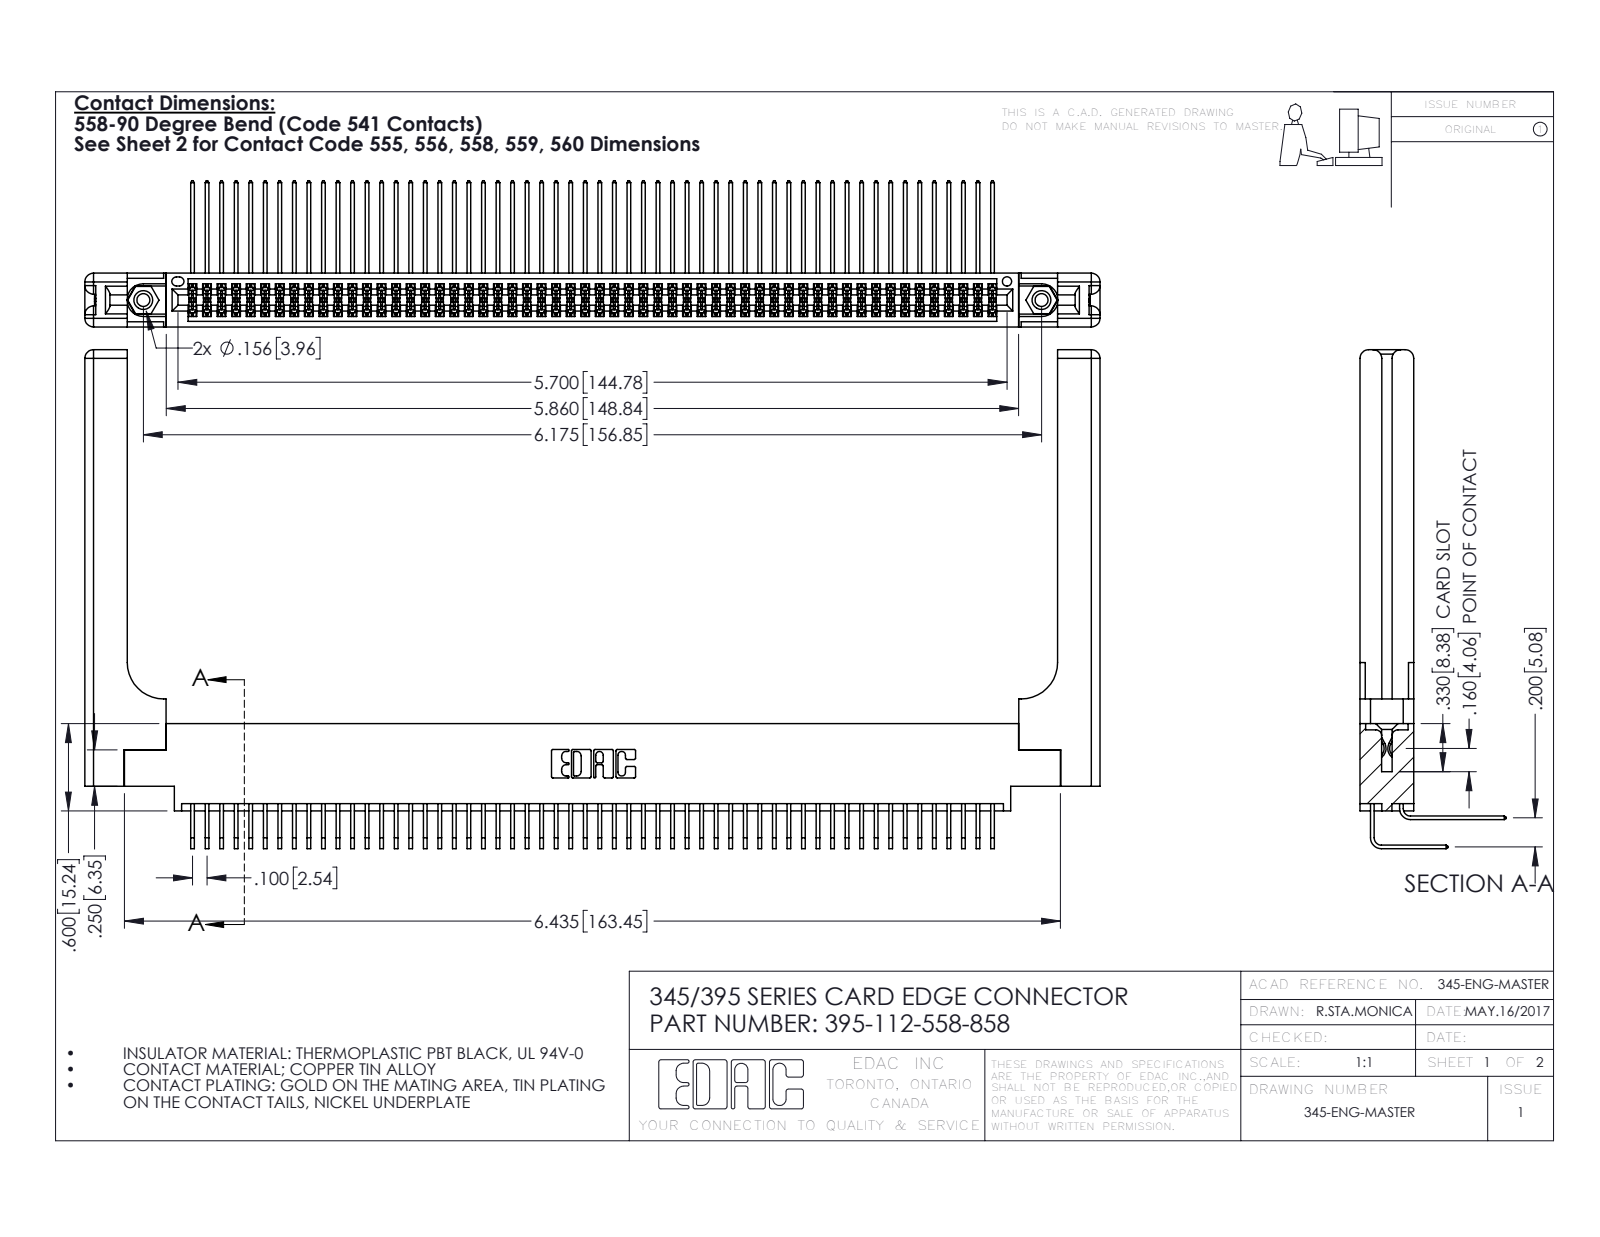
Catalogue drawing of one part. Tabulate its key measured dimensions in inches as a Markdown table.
| quantity | value |
| --- | --- |
| part name | 345-250-001_345-250-001-102; 345-220-058_345-220-058; 345 Part_0.170 Offset - 0.156 Dia-TH; 395-112-558-858 (+2 more) |
| STEP written by | SolidWorks 2016 (CONFIG_CONTROL_DESIGN) |
| units | inches |
| bodies | 117 solids, 6210 faces (4152 planar, 1998 cylindrical, 60 other) |
| overall size | 6.979 × 3.429 × 1.005 |
| volume | 1.608 in³ |
| surface area | 54.16 in² |
| round holes (diameter × count) | 0.089 × 2, 0.125 × 2, 0.156 × 2, 0.064 × 1 |
| round bosses / shafts (diameter × count) | 0.155 × 2 |
| partial cylindrical surfaces (radius × count) | 0.006 × 169, 0.01 × 22, 0.06 × 16, 0.007 × 6, 0.031 × 6, 0.026 × 3, 0.014 × 2, 0.019 × 2 |
| main face-to-face distances | 0.072, 0.298, 0.37, 0.2, 0.098, 0.272, 0.025, 0.225, 0.175, 0.148 |
| hole center spacings | 0.27, 5.939, 6.175 |
